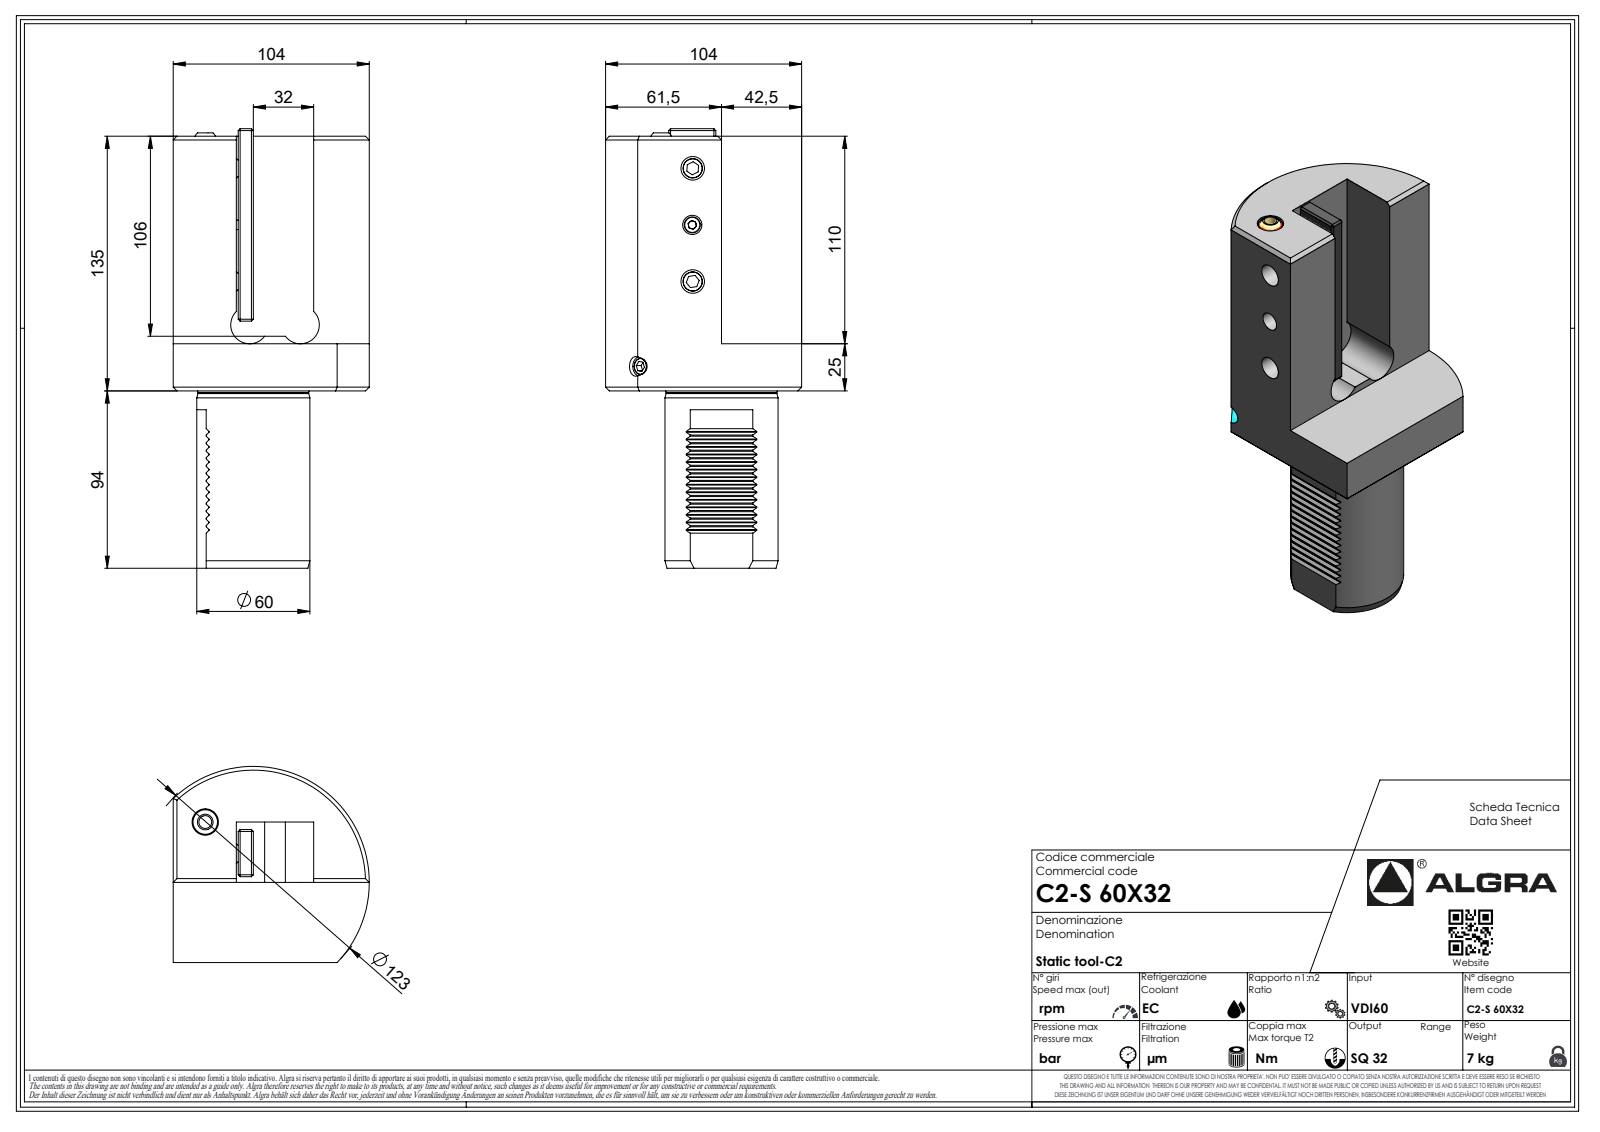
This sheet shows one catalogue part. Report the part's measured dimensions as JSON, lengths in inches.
{"part_name": "C2-S60X32", "step_written_by": "SolidWorks 2023 (AUTOMOTIVE_DESIGN)", "units": "inches", "bodies": {"solids": 1, "faces": 355, "planar": 226, "cylindrical": 46, "other": 83}, "overall_size": [9.173, 4.094, 4.094], "volume_in3": 58.45, "surface_area_in2": 141.9, "round_holes": [[0.083, 1]], "round_bosses_or_shafts": [[2.362, 1], [2.311, 1], [0.251, 1], [0.197, 1], [0.067, 1]], "partial_cylinders_radius": [[0.012, 14], [0.013, 7], [0.02, 7], [0.146, 7], [0.394, 2], [0.008, 1], [2.421, 1]], "face_to_face_distances": [1.26, 0.984, 2.933, 1.673, 4.331, 5.315, 1.614, 1.319, 3.701, 4.685]}
